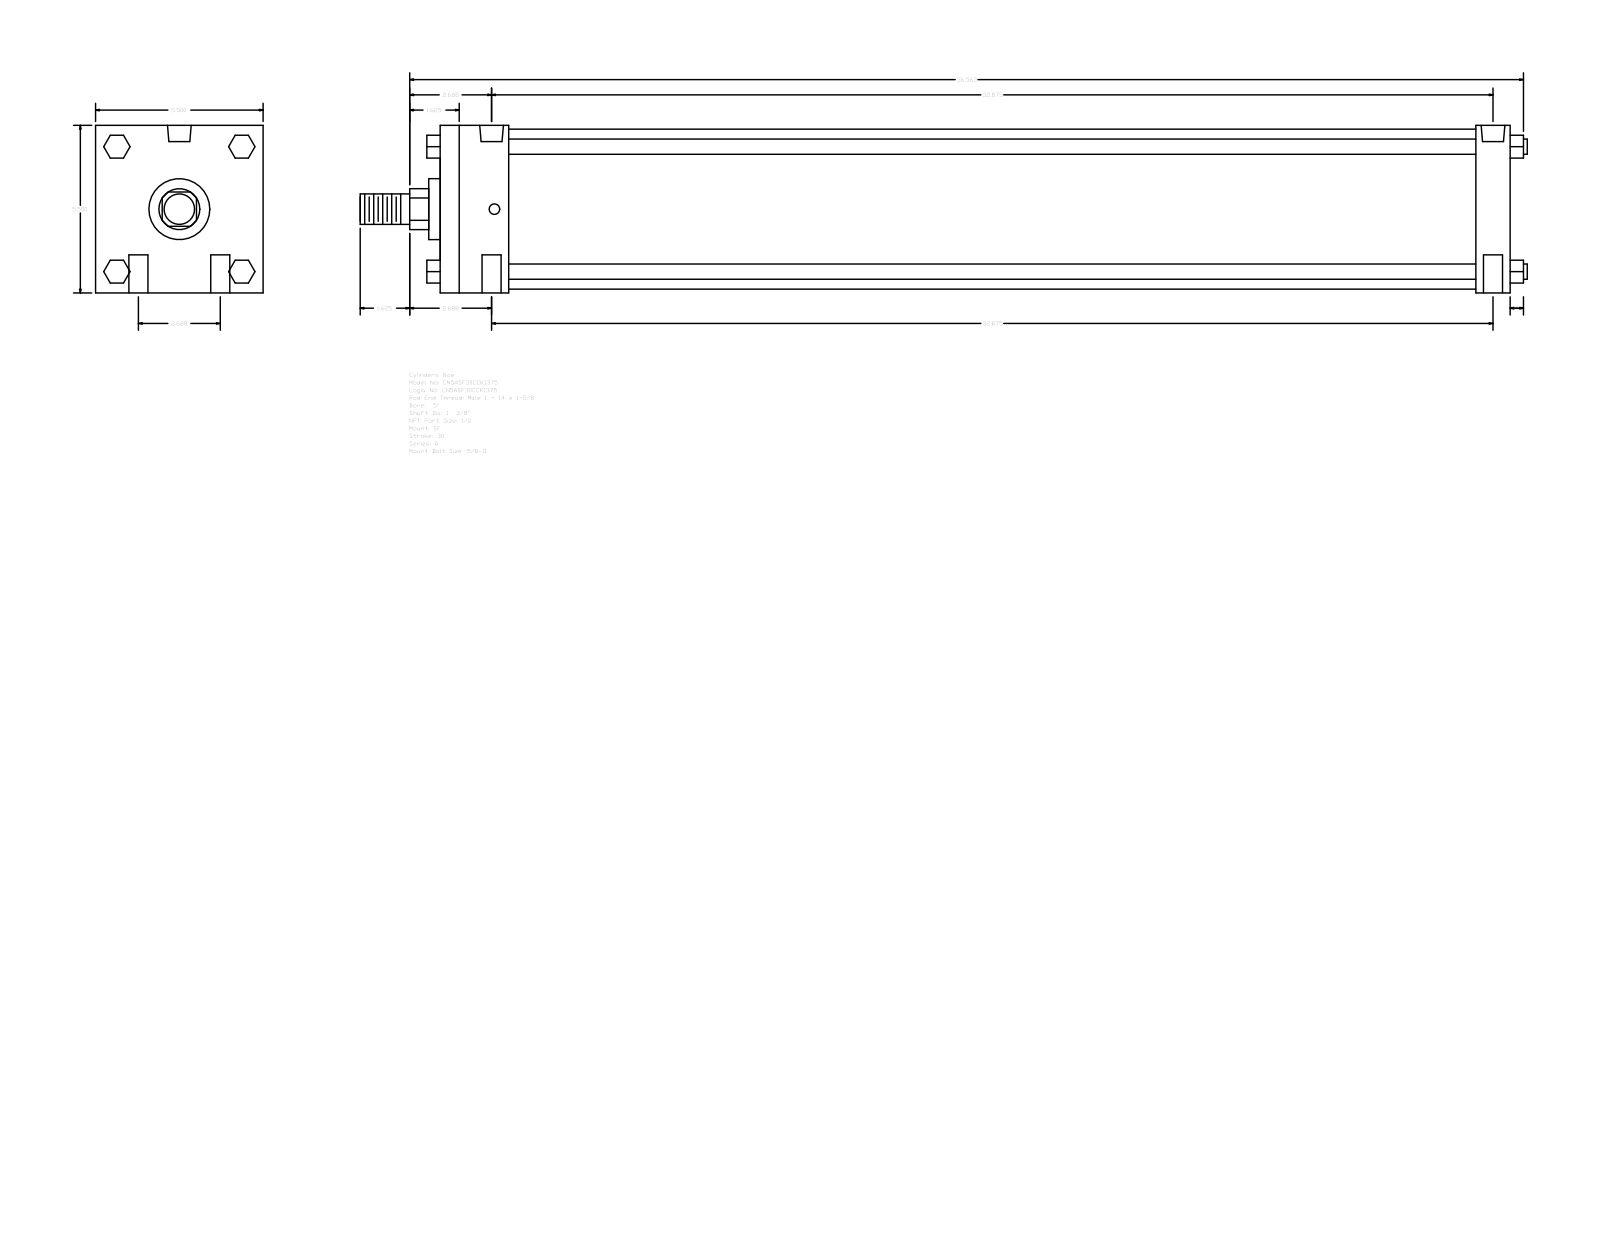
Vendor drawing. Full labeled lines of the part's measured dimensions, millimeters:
Part name (STEP PRODUCT): A_SF__0500_1.375
STEP written by: GSSL Pune (CONFIG_CONTROL_DESIGN)
Units: millimetres
Bodies: 0 solids, 124 faces (94 planar, 30 cylindrical, 0 other)
Overall size (bounding box): 973.14 × 139.7 × 139.7
Round holes (diameter × count): ⌀15.88 ×4, ⌀8.73 ×2, ⌀19.77 ×2
Round bosses / shafts (diameter × count): ⌀12.7 ×4, ⌀133.35 ×1, ⌀50.8 ×1, ⌀34.92 ×1, ⌀25.4 ×1
Partial cylindrical surfaces — rounded edges, fillets, slot ends (radius × count): R17.06 ×1
Main face-to-face distances: 139.7, 892.18, 57.15, 28.58, 863.6, 806.45, 835.03, 19.05, 52.07, 90.18
Hole centre spacings: 34.13, 835.73, 835.03, 68.26, 837.82, 830.25
